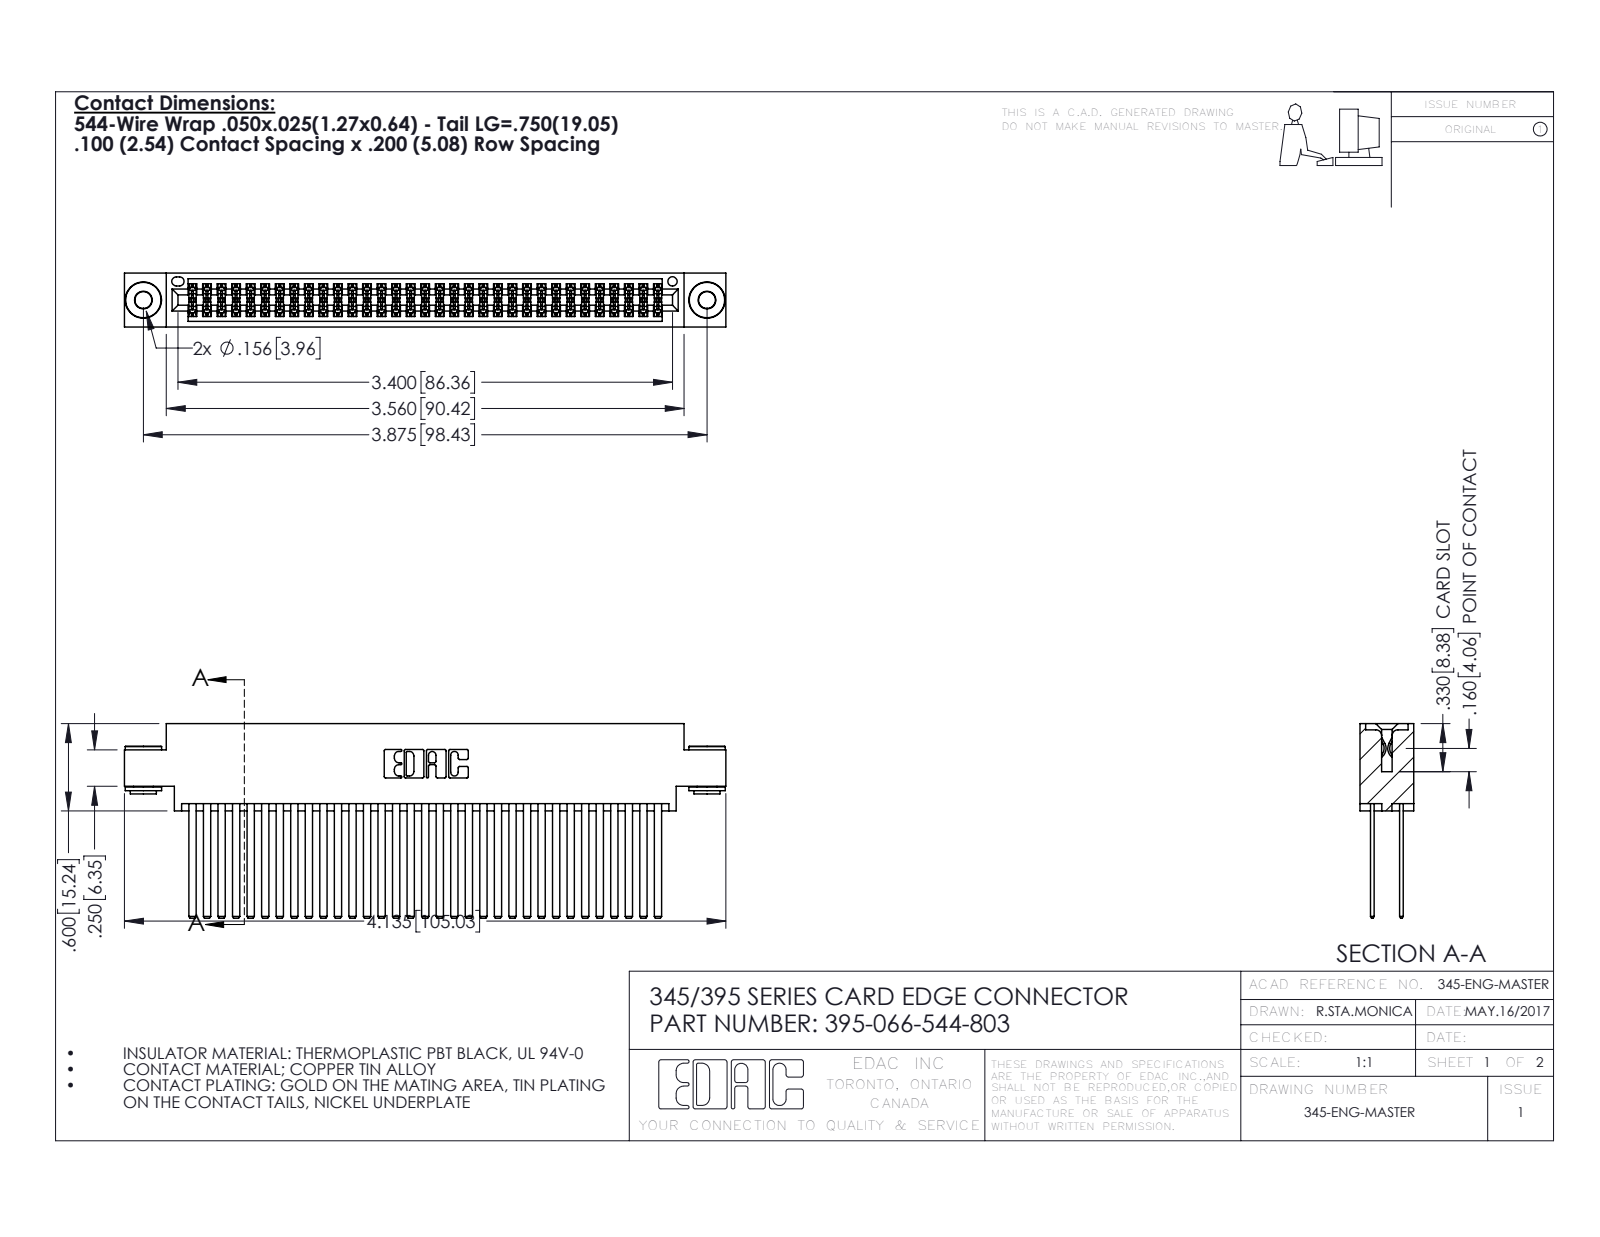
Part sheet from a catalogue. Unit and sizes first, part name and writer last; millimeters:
Units: millimetres
Overall size (bounding box): 105 × 34 × 9.4
Round holes (diameter × count): ⌀2.9 ×2, ⌀4 ×2, ⌀1.6 ×1
Round bosses / shafts (diameter × count): ⌀6.4 ×2, ⌀4.6 ×2, ⌀3.5 ×2
Partial cylindrical surfaces — rounded edges, fillets, slot ends (radius × count): R0.2 ×99, R0.3 ×22, R0.2 ×6, R0.8 ×6, R0.7 ×3, R0.4 ×2, R0.5 ×2, R0.6 ×2
Main face-to-face distances: 5.1, 0.6, 1.8, 2.5, 6.9, 7.6, 5.7, 4.4, 9.4, 3.8
Hole centre spacings: 6.9, 92.5, 98.4
Volume: 10 900 mm³ · Surface area: 19 070 mm²
Bodies: 69 solids, 3072 faces (2008 planar, 1056 cylindrical, 8 other)
Part name (STEP PRODUCT): 345-250-002_345-250-002-102; 345 Part_0.170 Offset - 0.156 Dia-TH; 395-066-544-803; 345-292-001_345-293-144
STEP written by: SolidWorks 2016 (CONFIG_CONTROL_DESIGN)
